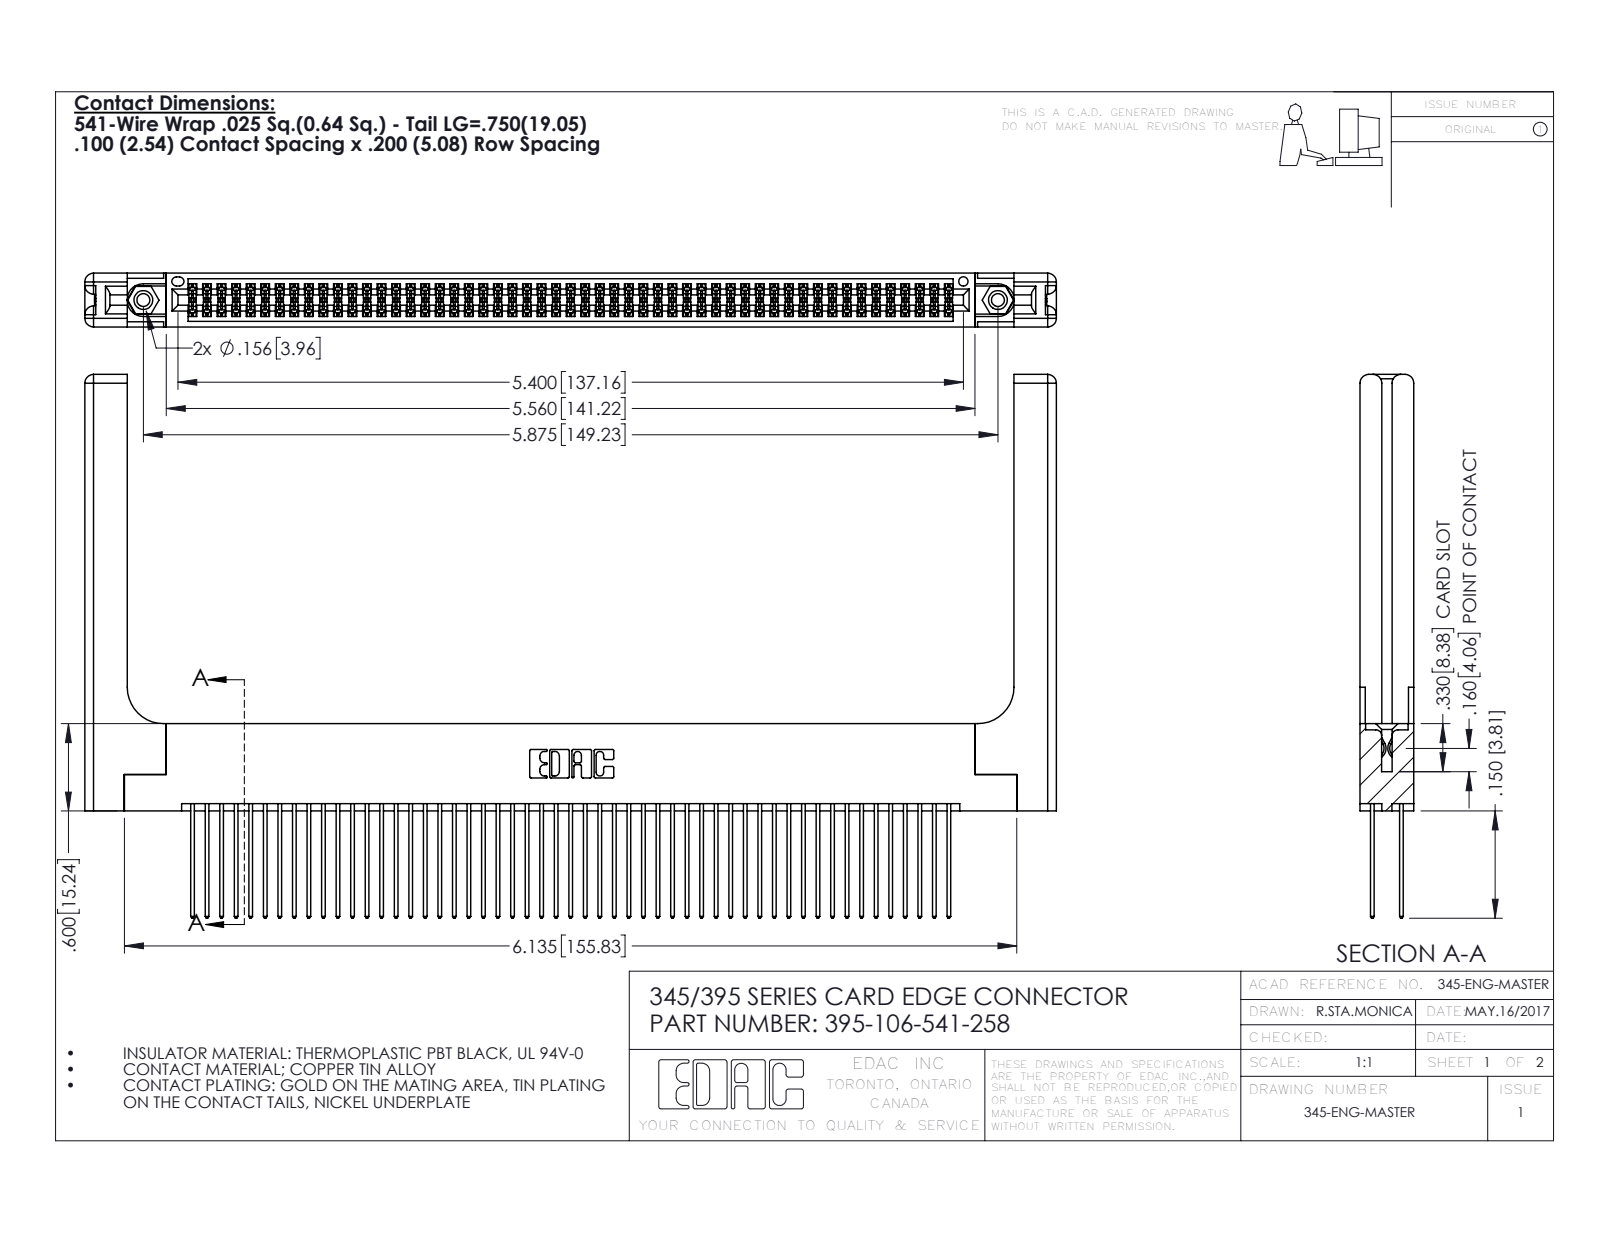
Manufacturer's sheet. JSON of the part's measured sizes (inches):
{"part_name": "345 Part_Flush Mounting Lugs - 0.156 Dia-TH; 345-250-001_345-250-001-102; 395-106-541-258; 345-292-001_345-293-141 (+1 more)", "step_written_by": "SolidWorks 2016 (CONFIG_CONTROL_DESIGN)", "units": "inches", "bodies": {"solids": 111, "faces": 5682, "planar": 3726, "cylindrical": 1896, "other": 60}, "overall_size": [6.679, 3.737, 0.37], "volume_in3": 1.566, "surface_area_in2": 51.99, "round_holes": [[0.089, 2], [0.125, 2], [0.156, 2], [0.064, 1]], "round_bosses_or_shafts": [[0.155, 2]], "partial_cylinders_radius": [[0.006, 159], [0.01, 106], [0.01, 22], [0.06, 16], [0.007, 6], [0.031, 6], [0.026, 3], [0.014, 2]], "face_to_face_distances": [0.072, 0.298, 0.2, 0.098, 0.272, 0.025, 0.37, 0.225, 0.175, 0.148], "hole_center_spacings": [0.27, 5.639, 5.875]}
